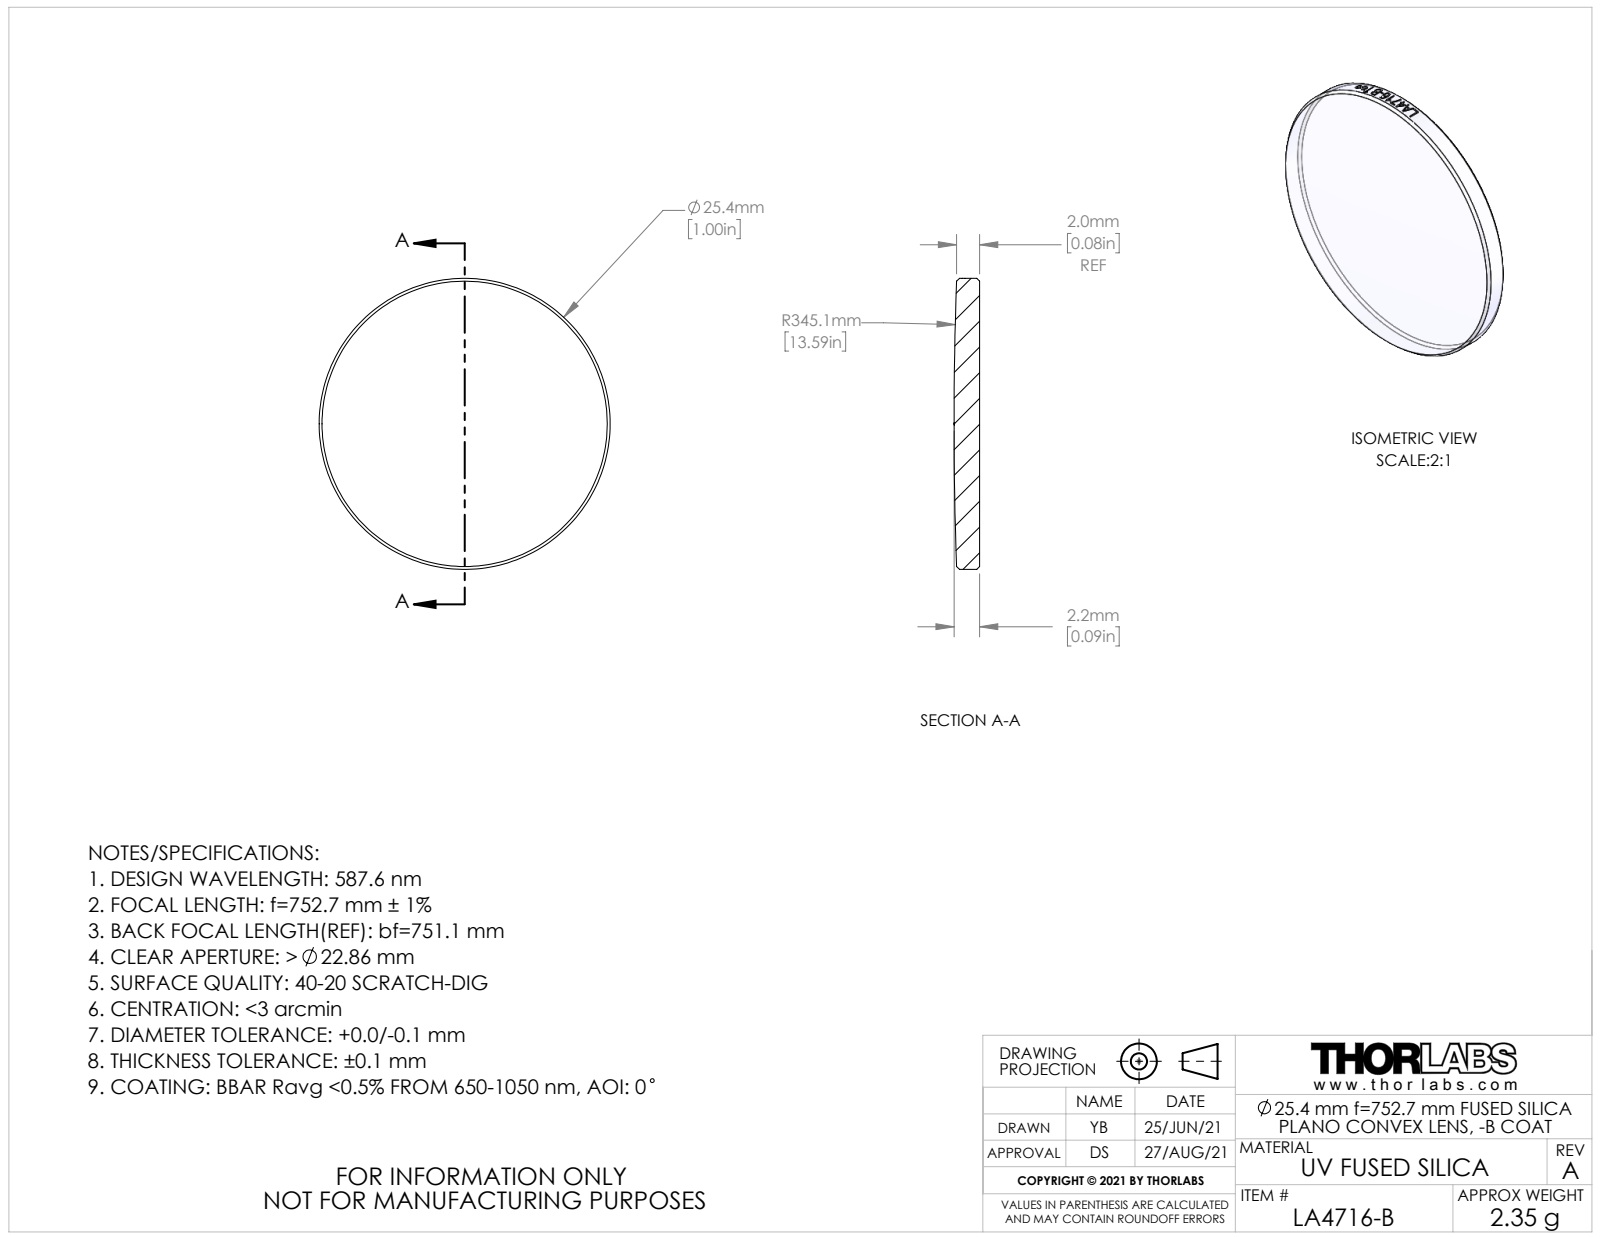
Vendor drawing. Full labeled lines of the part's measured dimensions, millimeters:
Part name (STEP PRODUCT): CTN017900-E0W
STEP written by: SolidWorks 2018 (AUTOMOTIVE_DESIGN)
Units: millimetres
Bodies: 1 solid, 26 faces (1 planar, 19 cylindrical, 6 other)
Overall size (bounding box): 25.4 × 25.4 × 2.23
Volume: 1 067 mm³ · Surface area: 1 150 mm²
Round bosses / shafts (diameter × count): ⌀25.4 ×1
